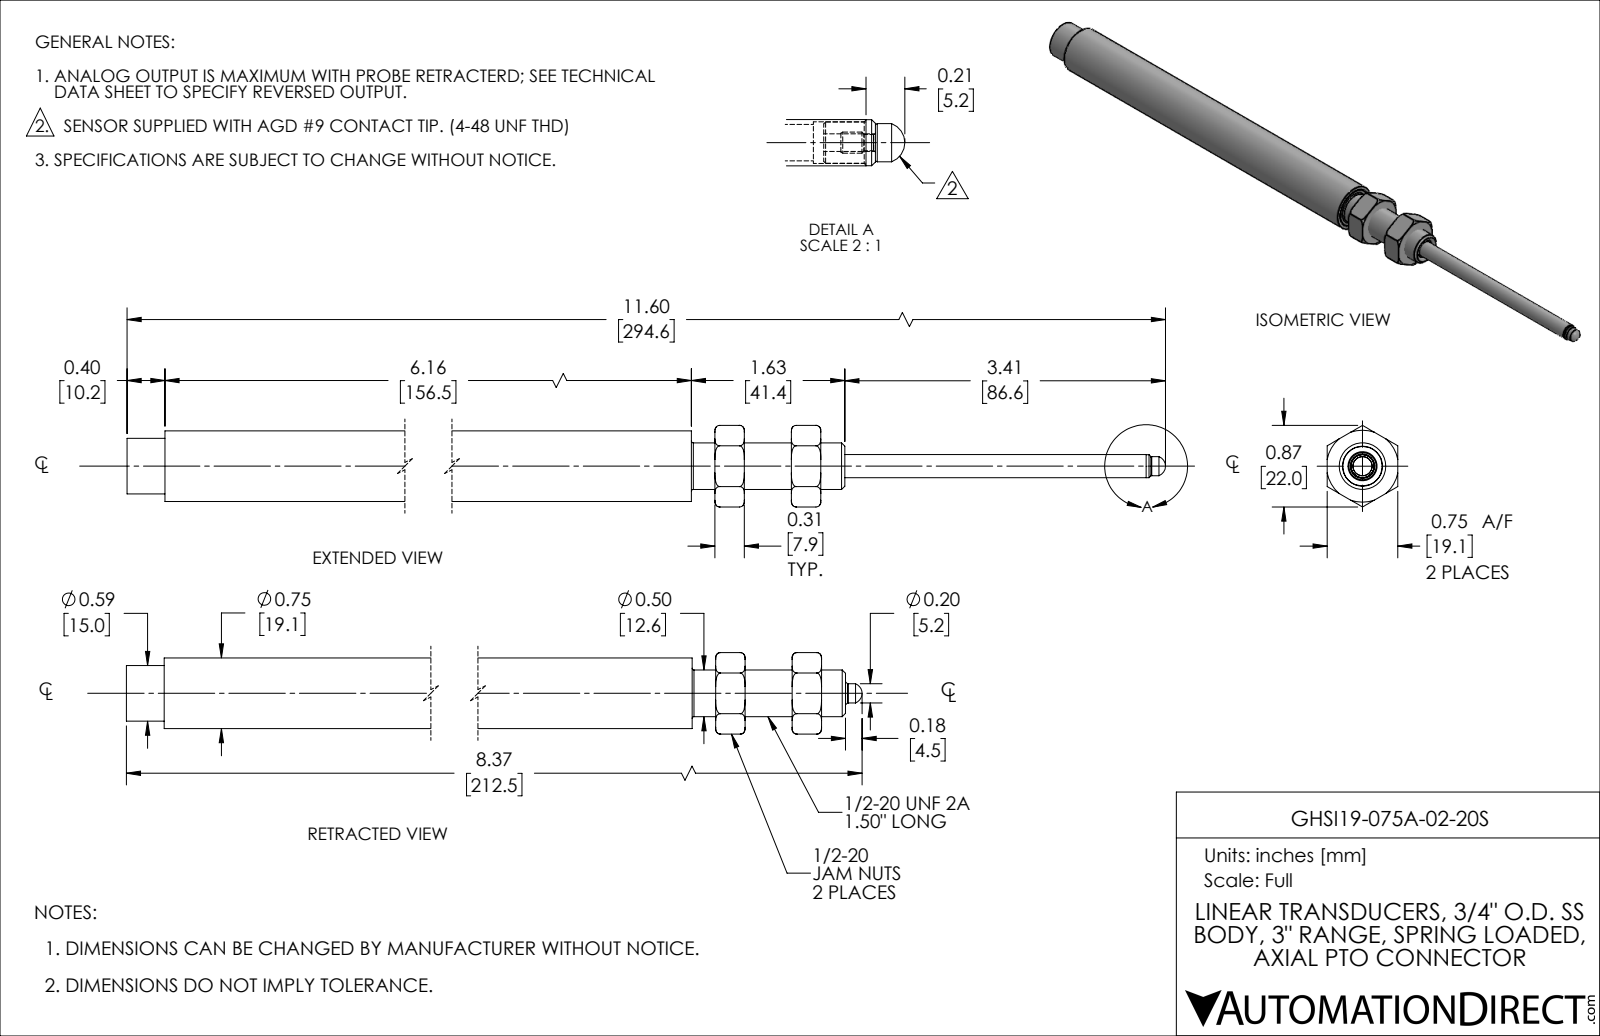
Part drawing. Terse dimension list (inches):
name: GHSE19-075A-02-20S_retracted
written by: SolidWorks 2019 (AUTOMOTIVE_DESIGN)
unit: in
bodies: 11 solids, 187 faces (77 planar, 65 cylindrical, 45 other)
size: 8.368 × 0.866 × 0.75
volume: 1.611 in³; area: 51.51 in²
holes: 1× ⌀0.093, 1× ⌀0.156, 1× ⌀0.193, 1× ⌀0.221, 1× ⌀0.249, 1× ⌀0.302, 1× ⌀0.31, 1× ⌀0.453, 1× ⌀0.52, 1× ⌀0.62, 1× ⌀0.625, 1× ⌀0.65
bosses: 6× ⌀0.03, 1× ⌀0.75, 1× ⌀0.725, 1× ⌀0.672, 1× ⌀0.624, 1× ⌀0.59, 1× ⌀0.495, 1× ⌀0.375
rounds: 2× R0.011, 2× R0.04, 1× R0.133, 1× R0.156, 1× R0.275
face distances: 0.813, 0.313, 0.75, 1.125, 0.5, 0.75, 6.432, 6.744, 7.244, 7.557
